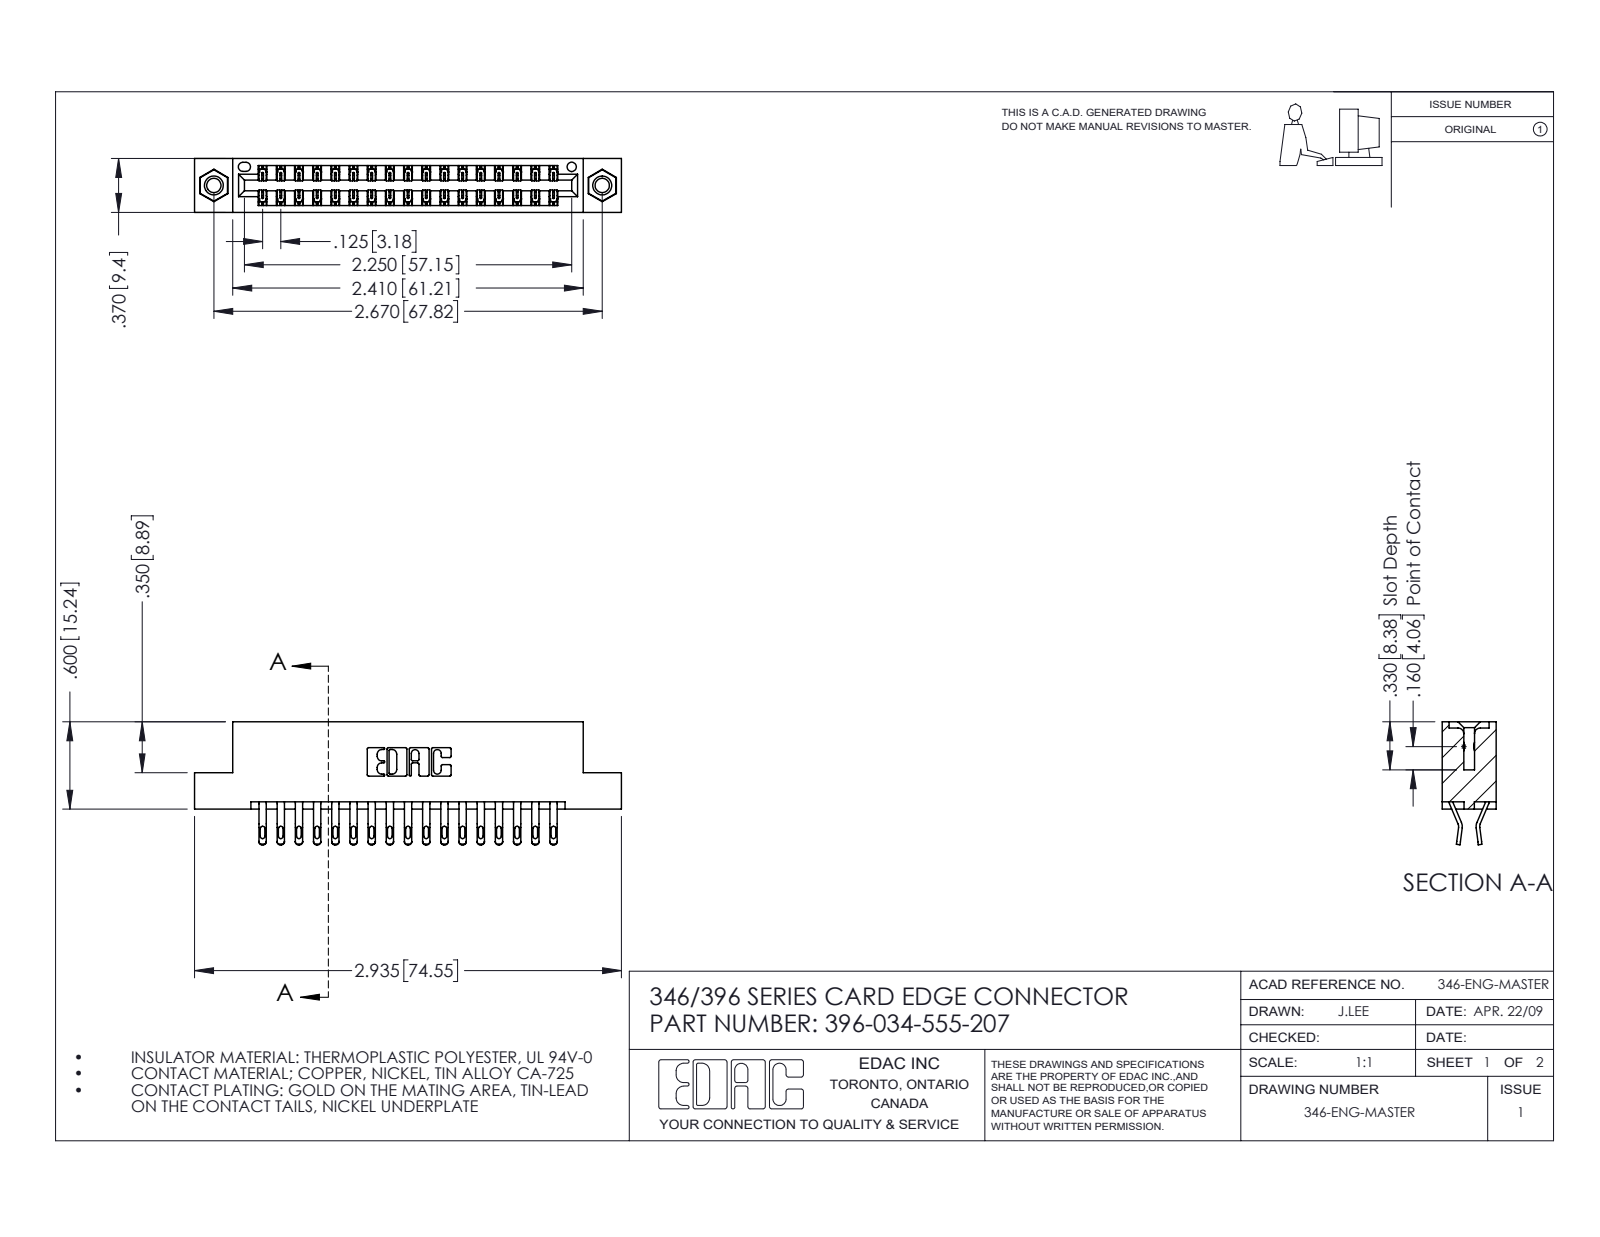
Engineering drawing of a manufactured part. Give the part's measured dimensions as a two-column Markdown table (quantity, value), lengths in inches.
| quantity | value |
| --- | --- |
| part name | 345-292-001_555 Tail; 396-034-555-207; 345-250-001_345-250-005-103; 346 Part_Flush Mounting Lugs - 0.156 Dia-TI |
| STEP written by | SolidWorks 2016 (CONFIG_CONTROL_DESIGN) |
| units | inches |
| bodies | 37 solids, 2154 faces (1230 planar, 908 cylindrical, 16 other) |
| overall size | 2.935 × 0.845 × 0.37 |
| volume | 0.437 in³ |
| surface area | 15.24 in² |
| round holes (diameter × count) | 0.098 × 2, 0.125 × 2, 0.156 × 2, 0.064 × 1 |
| round bosses / shafts (diameter × count) | 0.155 × 2 |
| partial cylindrical surfaces (radius × count) | 0.016 × 68, 0.02 × 68, 0.006 × 51, 0.01 × 22, 0.007 × 6, 0.031 × 6, 0.026 × 3, 0.01 × 2 |
| main face-to-face distances | 0.048, 0.322, 0.25, 0.37, 0.025, 0.072, 0.298, 0.275, 0.148, 0.222 |
| hole center spacings | 0.246, 2.463, 2.67 |
